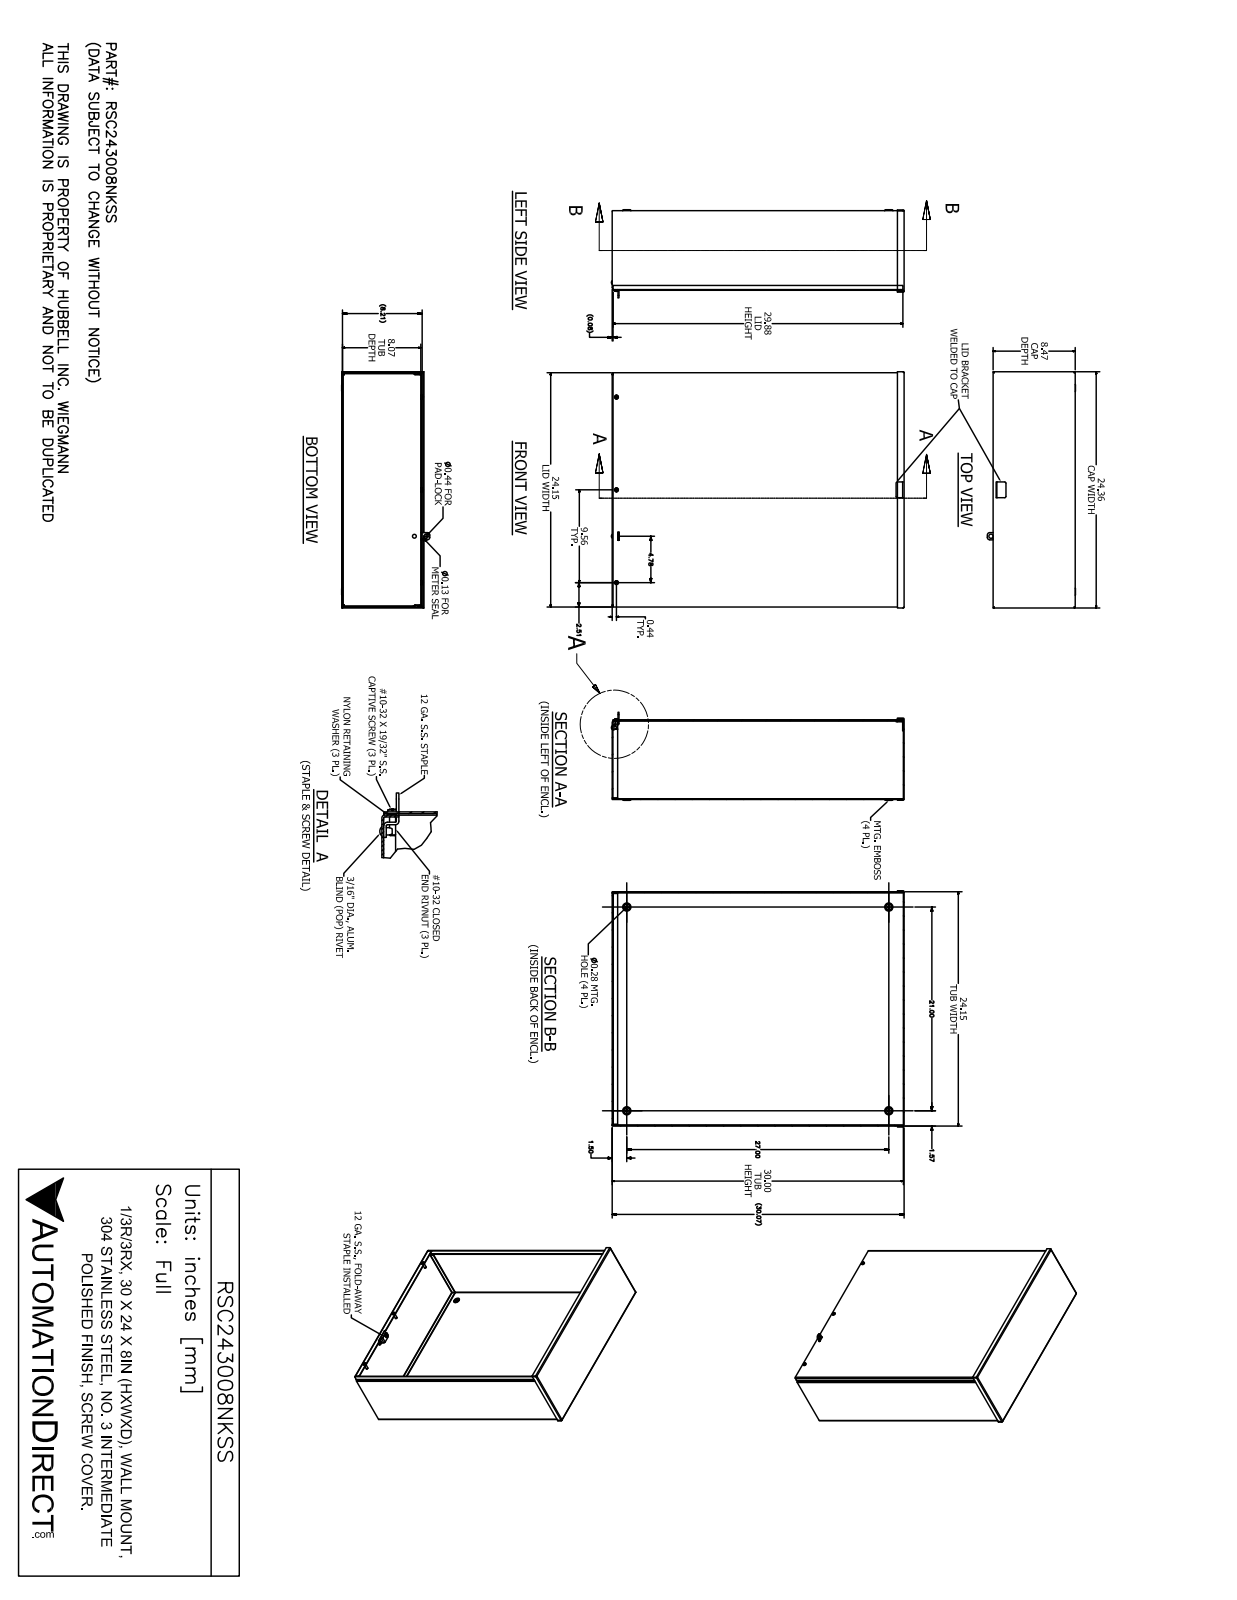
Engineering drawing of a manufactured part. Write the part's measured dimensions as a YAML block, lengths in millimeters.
part_name: "RSC243008NKSS"
step_written_by: "SolidWorks 2017 (AUTOMOTIVE_DESIGN)"
units: millimeters
bodies: {solids: 16, faces: 458, planar: 237, cylindrical: 113, other: 108}
overall_size: [766.2, 618.7, 230.7]
volume: 2938000
surface_area: 3148000
round_holes:
  - {diameter: 6.4, count: 6}
  - {diameter: 7.1, count: 4}
  - {diameter: 4, count: 3}
  - {diameter: 5, count: 3}
  - {diameter: 6.5, count: 3}
  - {diameter: 7.1, count: 3}
  - {diameter: 3.2, count: 1}
  - {diameter: 5, count: 1}
  - {diameter: 5.1, count: 1}
  - {diameter: 11.1, count: 1}
round_bosses_or_shafts:
  - {diameter: 11.5, count: 3}
  - {diameter: 10.3, count: 3}
  - {diameter: 6.3, count: 3}
  - {diameter: 4.2, count: 3}
  - {diameter: 4.7, count: 1}
partial_cylinders:
  - {radius: 0.8, count: 23}
  - {radius: 2.7, count: 17}
  - {radius: 3.2, count: 4}
  - {radius: 6.4, count: 4}
  - {radius: 1.6, count: 3}
  - {radius: 2.3, count: 3}
  - {radius: 1.2, count: 2}
  - {radius: 1.3, count: 2}
face_to_face_distances: [1.9, 206.6, 208.4, 204.7, 611.5, 762, 613.4, 609.6, 763.9, 760.1]
hole_center_spacings: [242.9, 779.4, 740.6, 36, 36.6, 268.1, 268.1, 485.8]
